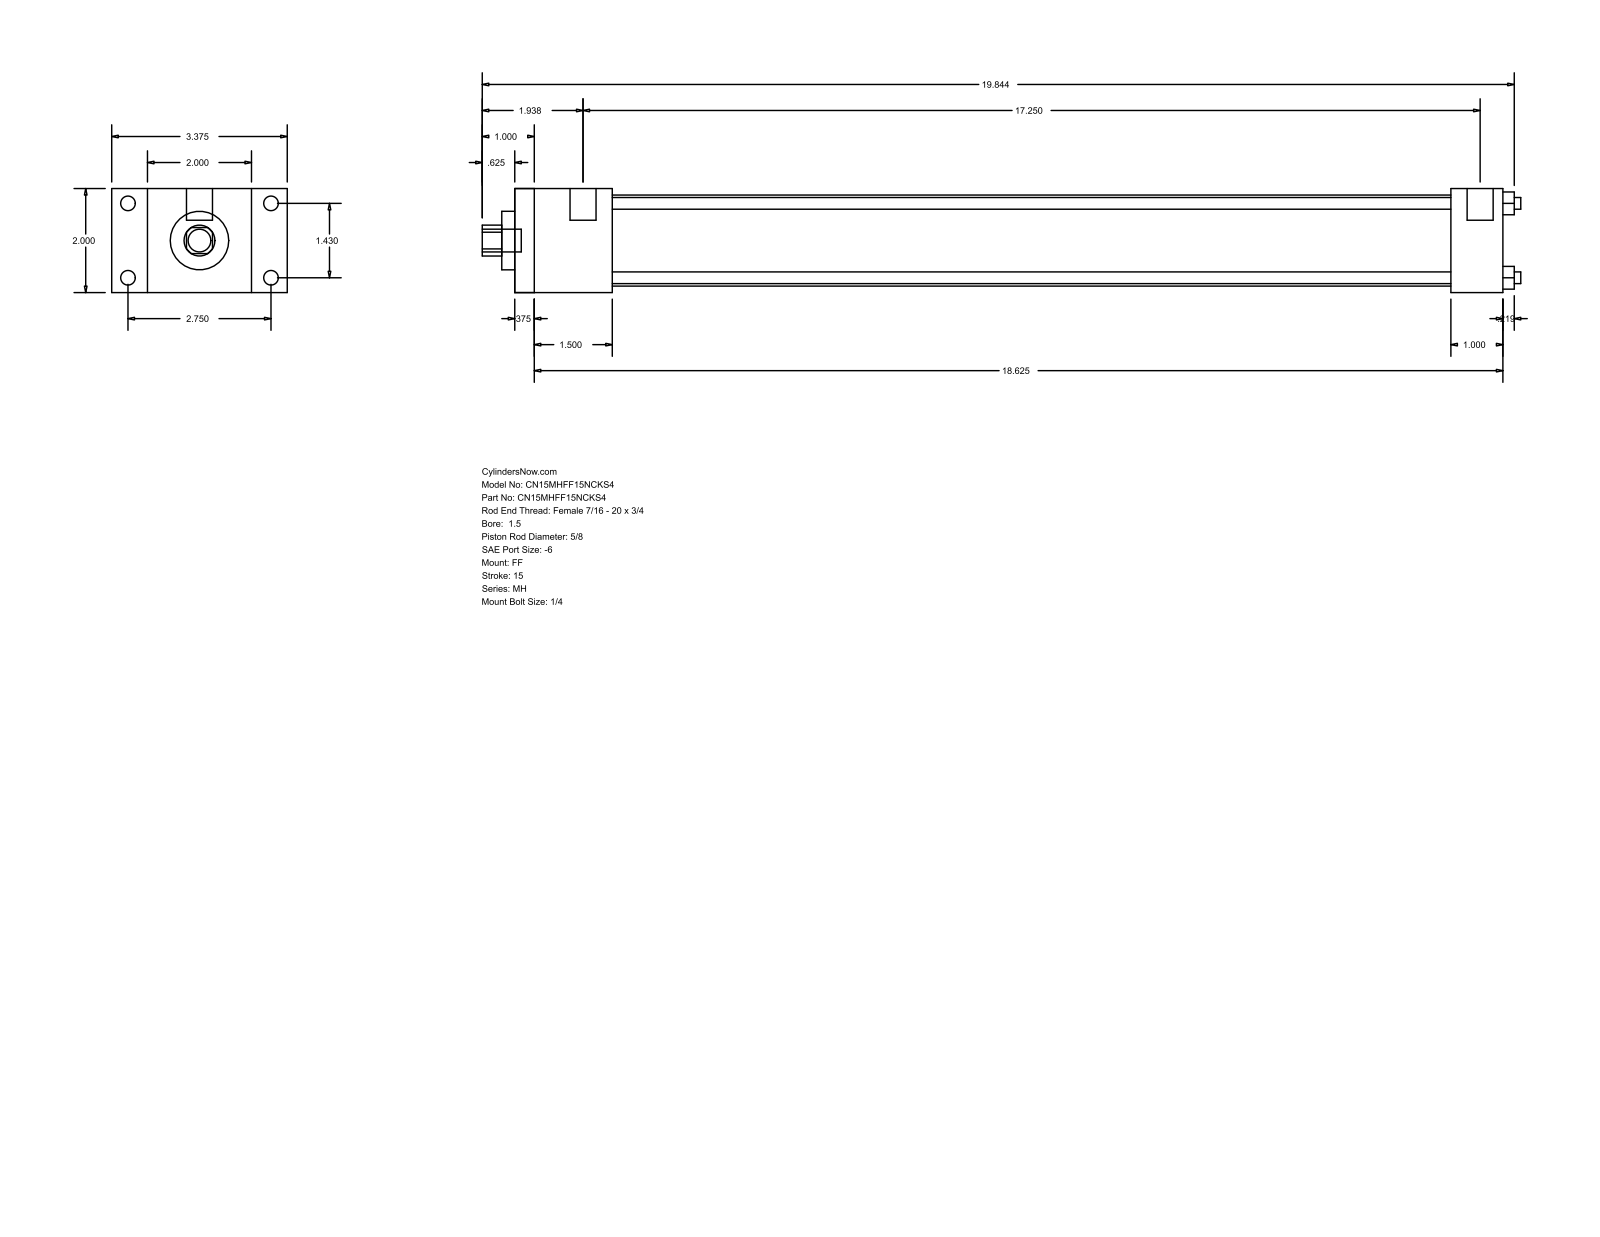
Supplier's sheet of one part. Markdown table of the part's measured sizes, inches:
| quantity | value |
| --- | --- |
| part name | MH_FF__0150_0.625 |
| STEP written by | GSSL Pune (CONFIG_CONTROL_DESIGN) |
| units | inches |
| bodies | 0 solids, 92 faces (64 planar, 28 cylindrical, 0 other) |
| overall size | 19.969 × 3.375 × 2 |
| round holes (diameter × count) | 0.225 × 4, 0.625 × 1, 1.125 × 1, 1.75 × 1 |
| round bosses / shafts (diameter × count) | 0.281 × 4, 0.219 × 4, 0.5 × 2, 0.437 × 1 |
| partial cylindrical surfaces (radius × count) | 0.297 × 1 |
| main face-to-face distances | 2, 19, 0.375, 18.625, 0.687, 2.687, 1.875, 1.5, 17.125, 18 |
| hole center spacings | 1.011, 1.43, 2.022 |
